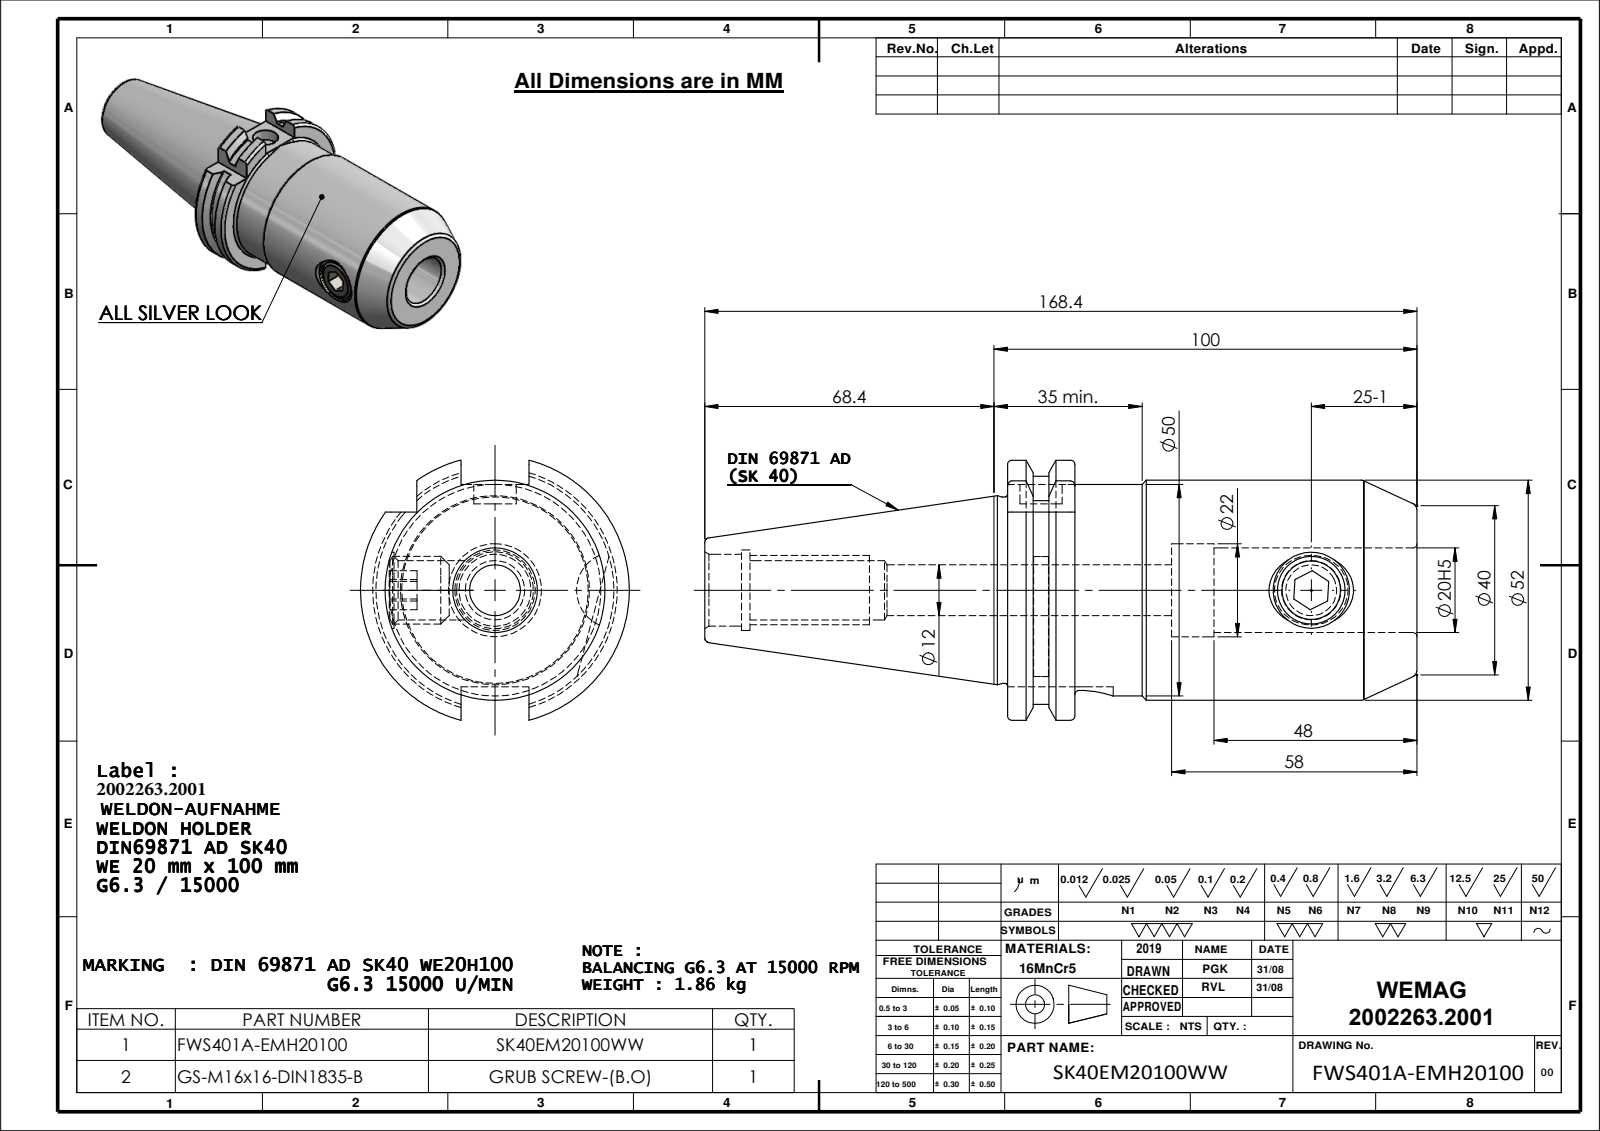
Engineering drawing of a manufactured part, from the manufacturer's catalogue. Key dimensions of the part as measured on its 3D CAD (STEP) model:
Part name (STEP PRODUCT): SK40TMH10094FWW
STEP written by: SolidWorks 2018 (CONFIG_CONTROL_DESIGN)
Units: millimetres
Bodies: 1 solid, 98 faces (30 planar, 32 cylindrical, 36 other)
Overall size (bounding box): 162.5 × 63.55 × 61.48
Volume: 125 912 mm³ · Surface area: 27 465 mm²
Round holes (diameter × count): ⌀3.3 ×1, ⌀8.5 ×1, ⌀10 ×1, ⌀10.5 ×1, ⌀11.1 ×1, ⌀14 ×1, ⌀17 ×1, ⌀19 ×1
Round bosses / shafts (diameter × count): ⌀44.45 ×1
Partial cylindrical surfaces — rounded edges, fillets, slot ends (radius × count): R28.12 ×1, R31.77 ×1
Main face-to-face distances: 15.9, 16.1, 47.8, 81.25, 71.6, 87.5, 162.5, 90.9, 75, 10.7
